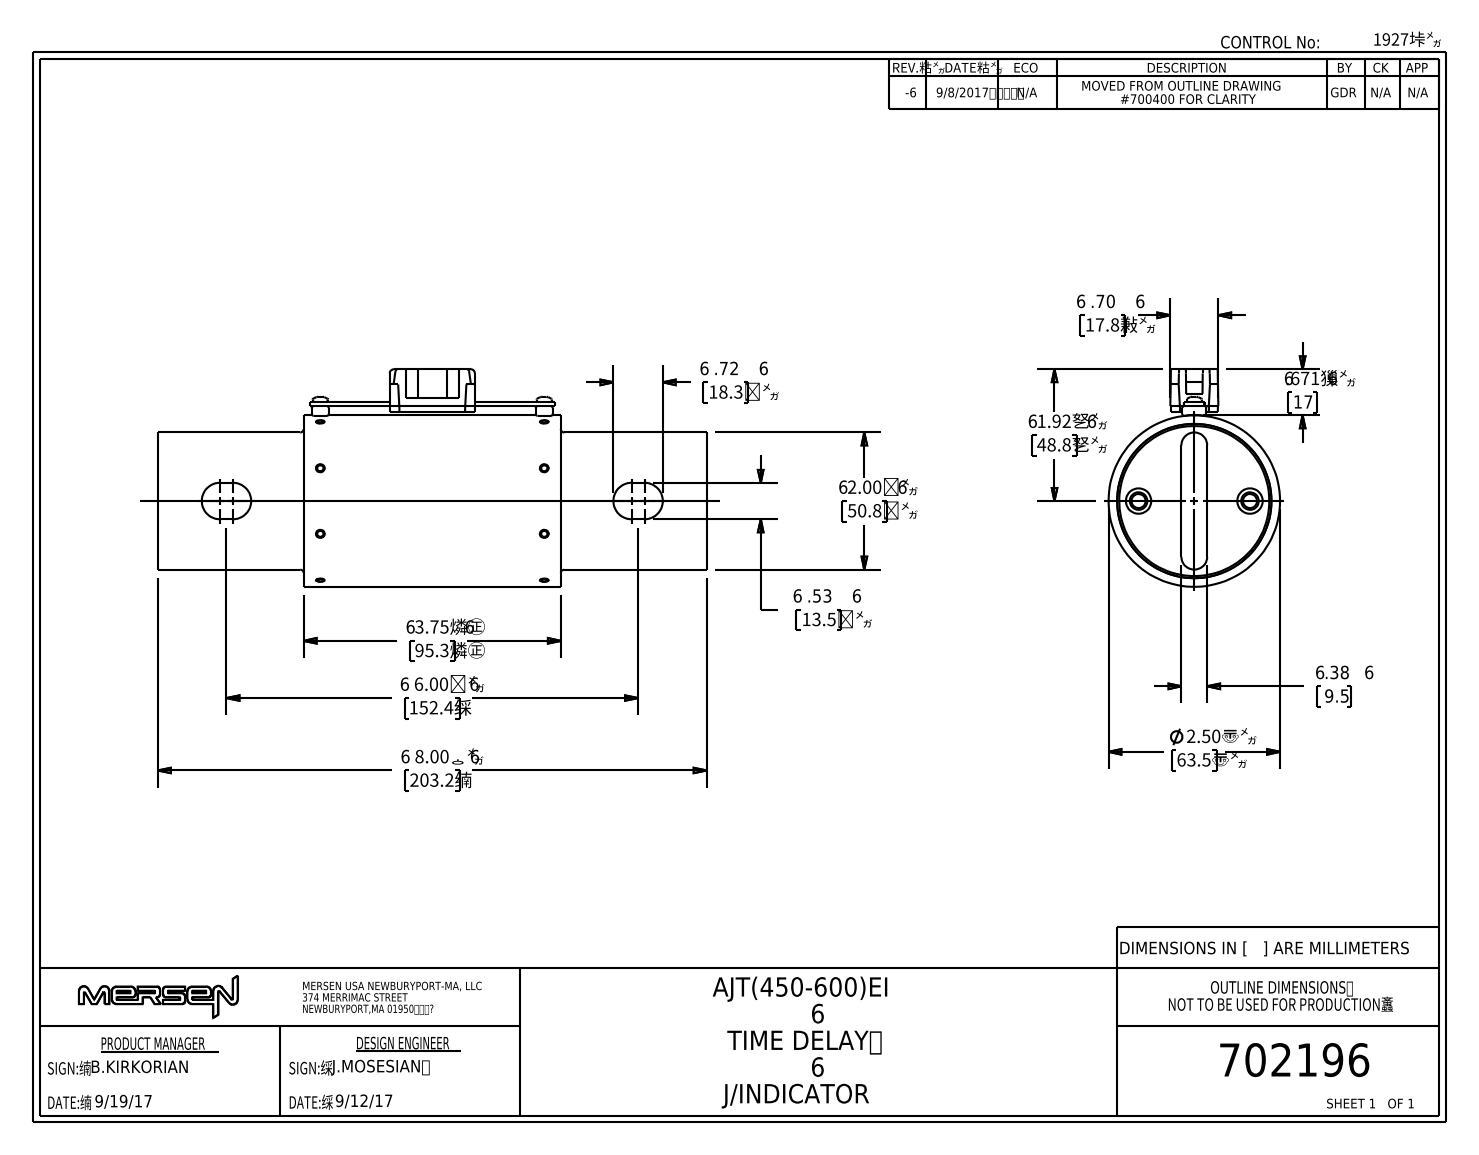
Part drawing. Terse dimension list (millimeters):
name: 702196rev
written by: SolidWorks 2016 (AUTOMOTIVE_DESIGN)
unit: mm
bodies: 34 solids, 2172 faces (788 planar, 759 cylindrical, 625 other)
size: 203.2 × 80.5 × 63.5
volume: 165 200 mm³; area: 77 740 mm²
holes: 16× ⌀3.2, 3× ⌀4.3, 2× ⌀2.6, 2× ⌀3.2, 2× ⌀5.2, 2× ⌀6.4, 1× ⌀57.2
bosses: 16× ⌀3.2, 2× ⌀6.5, 2× ⌀5.6, 2× ⌀2.8, 2× ⌀2, 1× ⌀63.5, 1× ⌀57.1, 1× ⌀9.3
rounds: 68× R101.6, 20× R0.8, 14× R0.1, 10× R0.5, 10× R1.5, 4× R1.3, 4× R1.8, 4× R6.8
face distances: 11.1, 84.1, 9.5, 95.3, 73, 6.4, 54, 65.1, 138.1, 149.2
hole spacings: 82.9, 20.6, 36.6, 46.3, 4.8, 4.8, 9.7, 41.2
